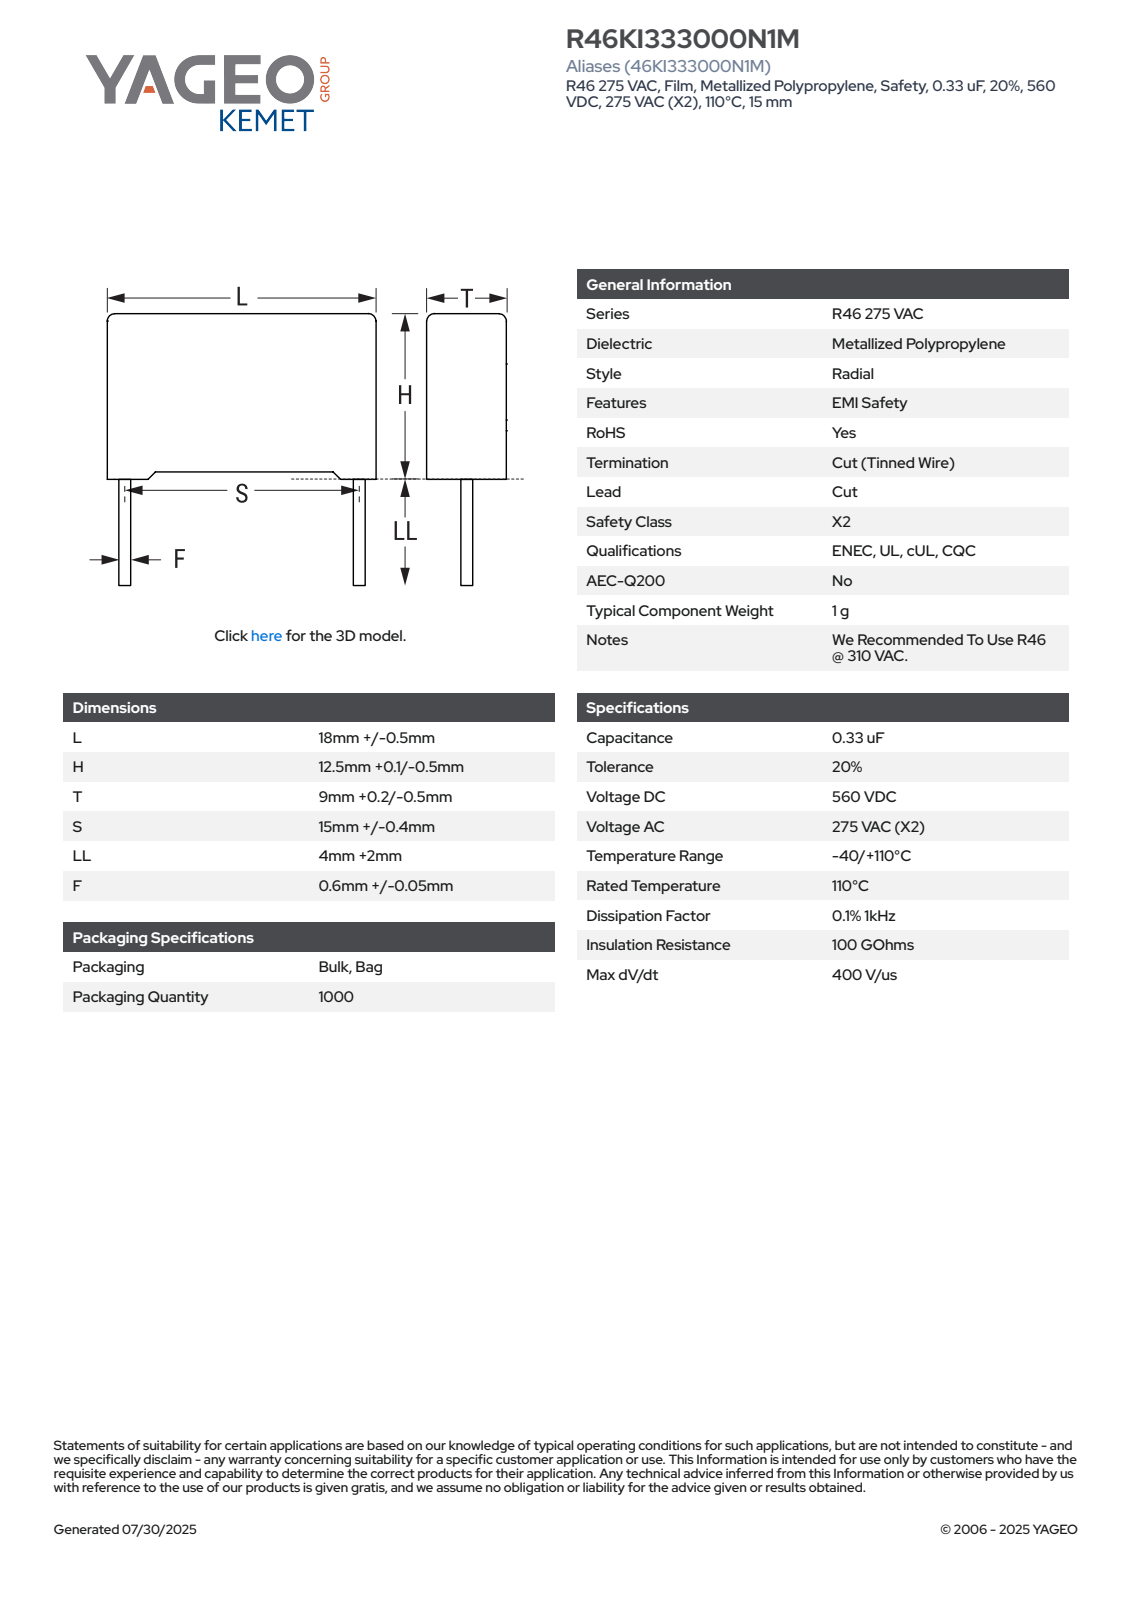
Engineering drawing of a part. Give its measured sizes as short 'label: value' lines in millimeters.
name: CFR_RB2_18X12.5X9_L18.5H12.6T9.2S15LL6F0.65
written by: SolidWorks 2021 (AUTOMOTIVE_DESIGN)
unit: mm
bodies: 4 solids, 85 faces (77 planar, 8 cylindrical, 0 other)
size: 18.6 × 18.5 × 9.21
volume: 2 037 mm³; area: 1 098 mm²
bosses: 2× ⌀0.65
rounds: 4× R0.5
face distances: 9.2, 11.85, 18.5, 0.62, 0.75, 12.6, 8.58, 0.43, 0.32, 12.17
